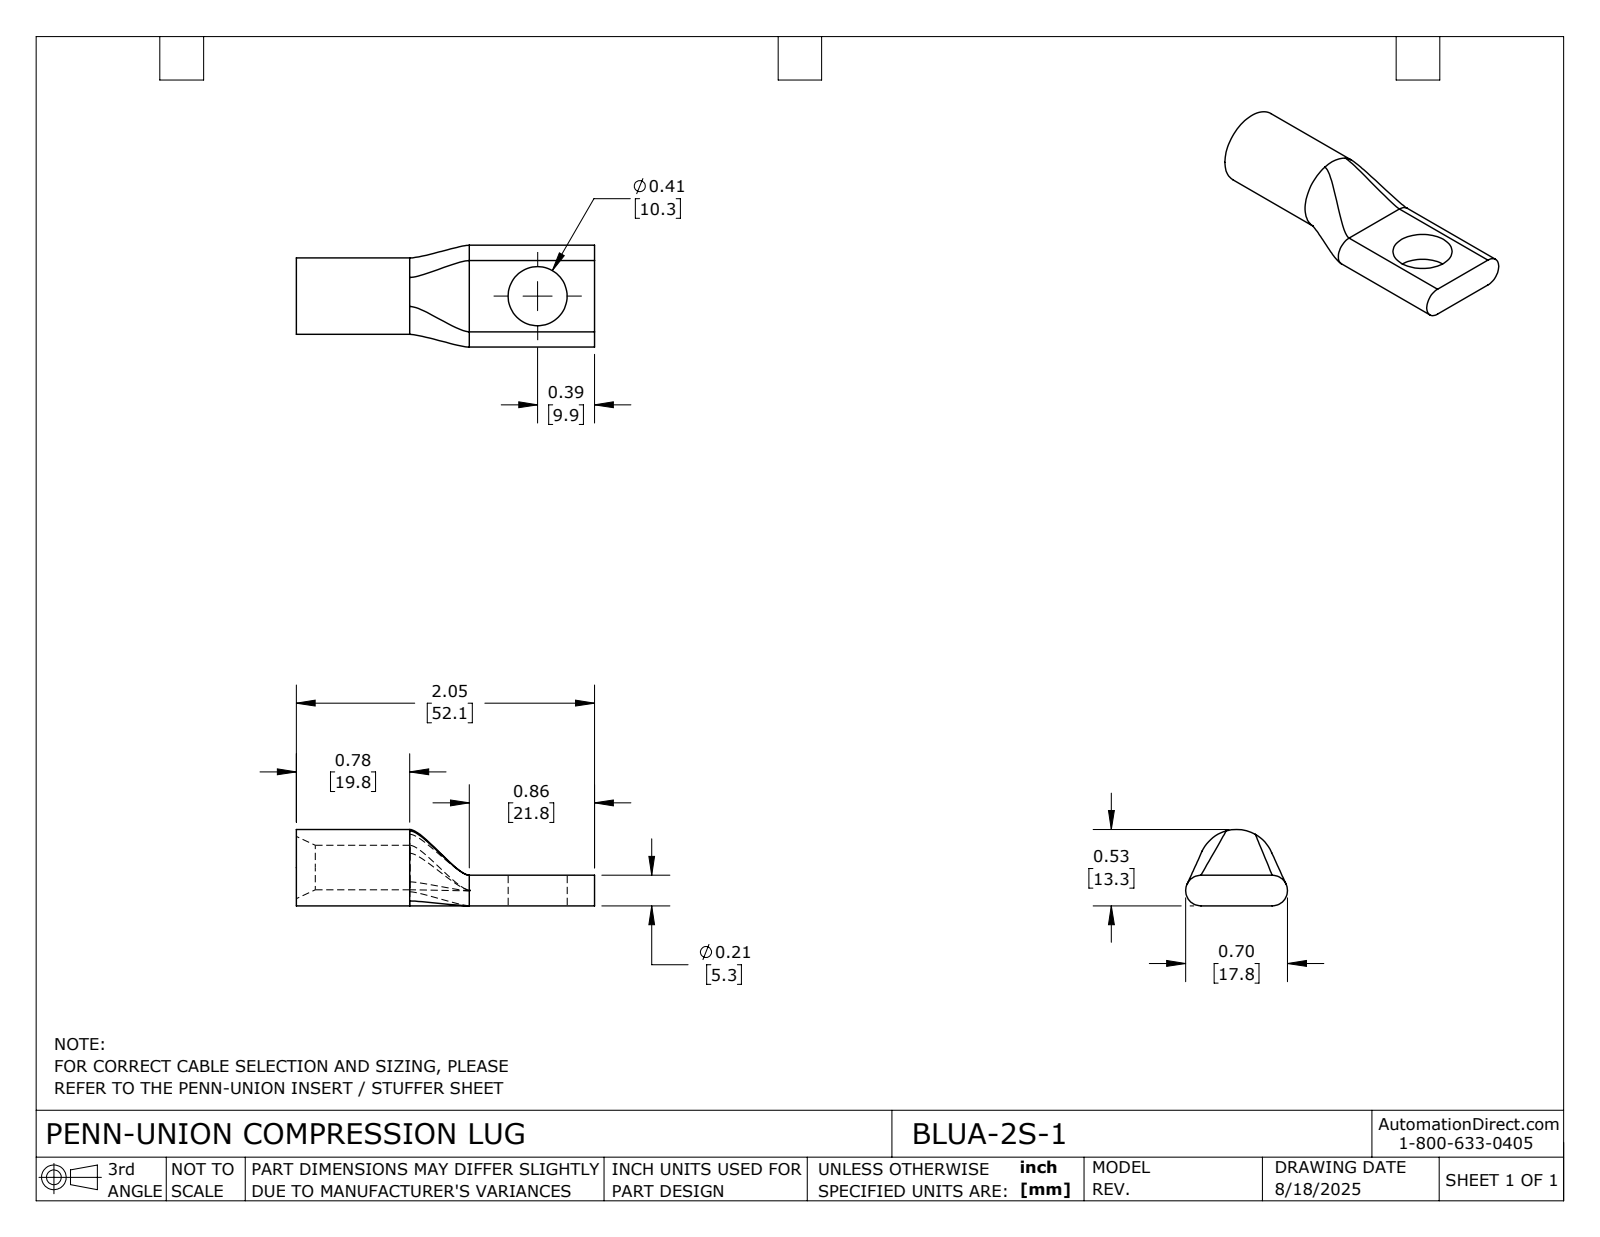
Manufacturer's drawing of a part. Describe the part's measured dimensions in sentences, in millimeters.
The part is named "BLUA-2S-1". Its 3-D file was written by "SolidWorks 2024 (CONFIG_CONTROL_DESIGN)". It is 1 solid with 24 faces: 5 planar, 9 cylindrical and 10 other. Overall it measures 52.1 by 17.8 by 13.3 millimeters. Its volume is 4 180 cubic millimeters and its surface area 3 137 square millimeters. Round holes: 1 of diameter 7.8, 1 of diameter 10.3. Round bosses or shafts: 1 of diameter 13.3. Partial cylindrical surfaces (rounded edges, fillets, slot ends): 2 of radius 2.7. The main face-to-face distances are 5.3, 52.1, 30.2, 21.8.
